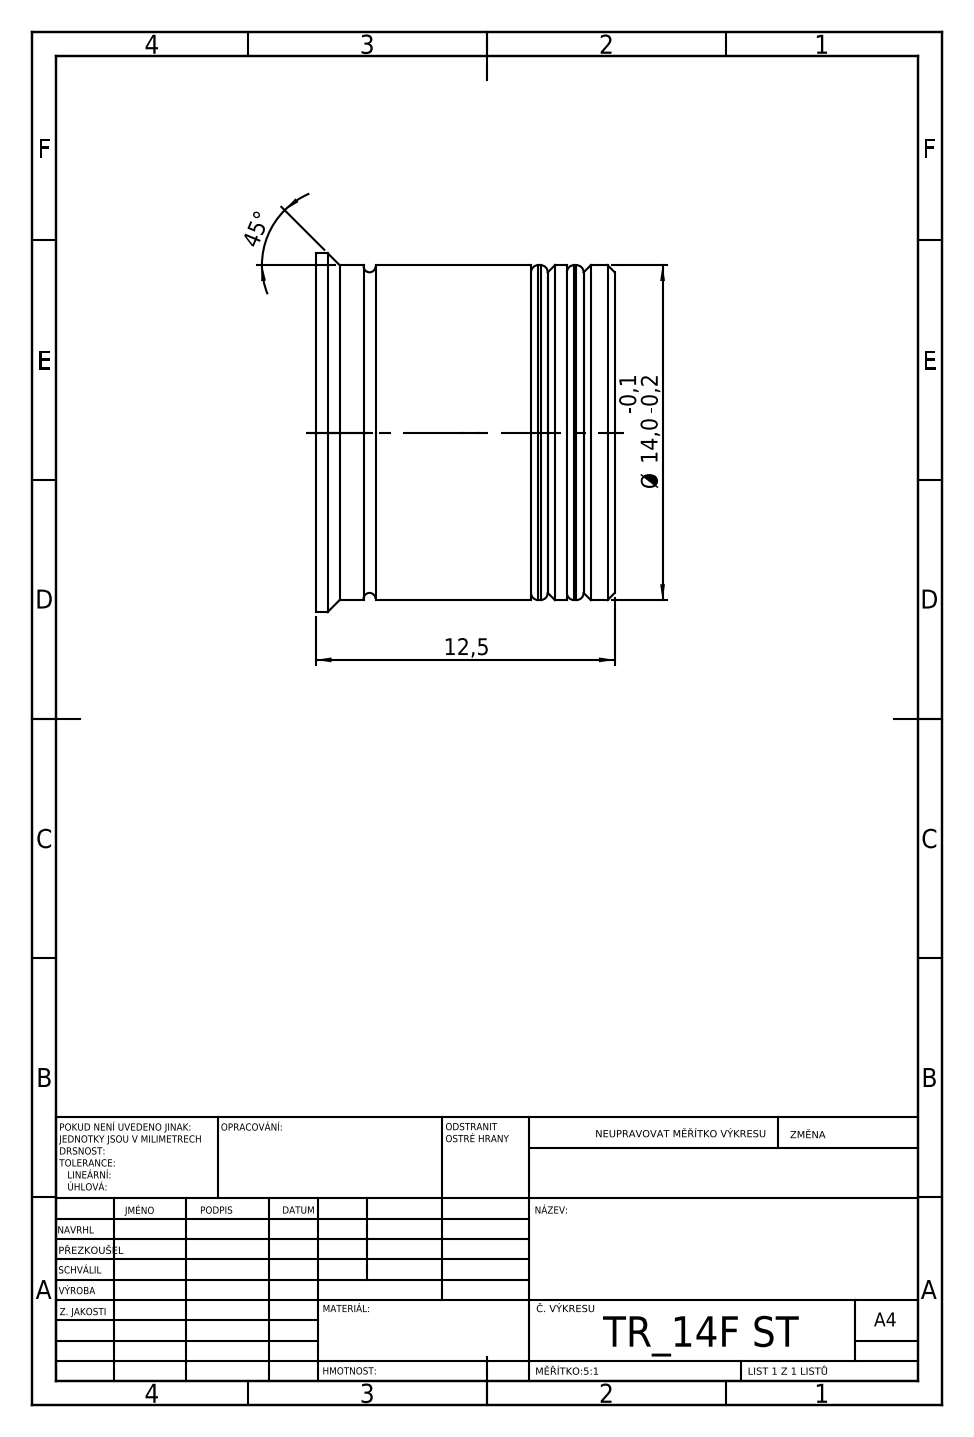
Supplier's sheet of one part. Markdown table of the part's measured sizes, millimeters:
| quantity | value |
| --- | --- |
| STEP written by | SolidWorks 2019 (CONFIG_CONTROL_DESIGN) |
| units | millimeters |
| bodies | 3 solids, 74 faces (29 planar, 25 cylindrical, 20 other) |
| overall size | 15 × 15 × 12.5 |
| volume | 2 009 mm³ |
| surface area | 1 686 mm² |
| round bosses / shafts (diameter × count) | 15 × 1, 14 × 1, 13.4 × 1, 11 × 1 |
| main face-to-face distances | 1.5, 0.7, 2, 2.2, 0.8, 1.3, 2.8, 3.5, 8.7, 8 |
